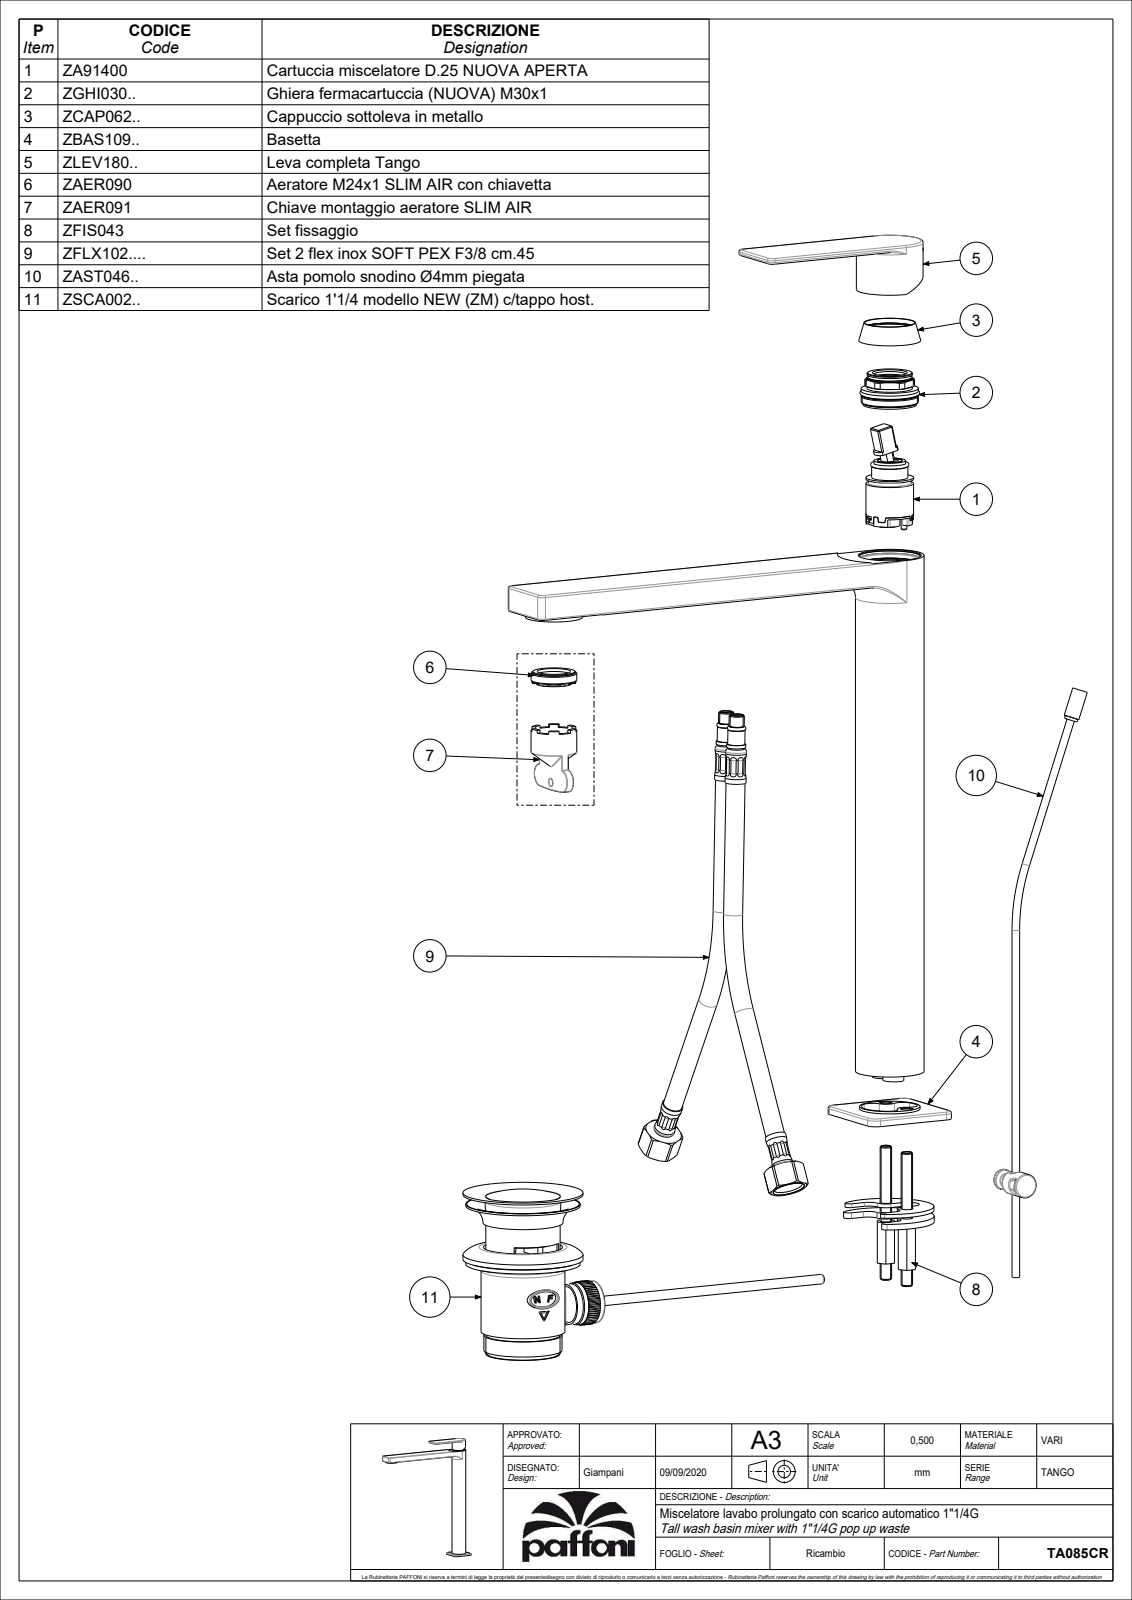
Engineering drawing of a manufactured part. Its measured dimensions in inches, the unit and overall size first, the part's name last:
Units: inches
Overall size (bounding box): 12.094 × 10.276 × 1.969
Round bosses / shafts (diameter × count): ⌀1.417 ×1, ⌀1.378 ×1, ⌀1.181 ×1, ⌀0.728 ×1, ⌀0.315 ×1, ⌀0.299 ×1, ⌀0.157 ×1
Partial cylindrical surfaces — rounded edges, fillets, slot ends (radius × count): R0.039 ×16, R0.118 ×4, R0.197 ×4, R0.031 ×2
Main face-to-face distances: 0.531, 1.622, 1.091, 1.417, 10.472, 11.004, 12.094, 0.157, 10.315, 10.846
Bodies: 0 solids, 93 faces (22 planar, 40 cylindrical, 31 other)
Part name (STEP PRODUCT): TA085CR
STEP written by: CREO PARAMETRIC BY PTC INC, 2020044 (CONFIG_CONTROL_DESIGN)
